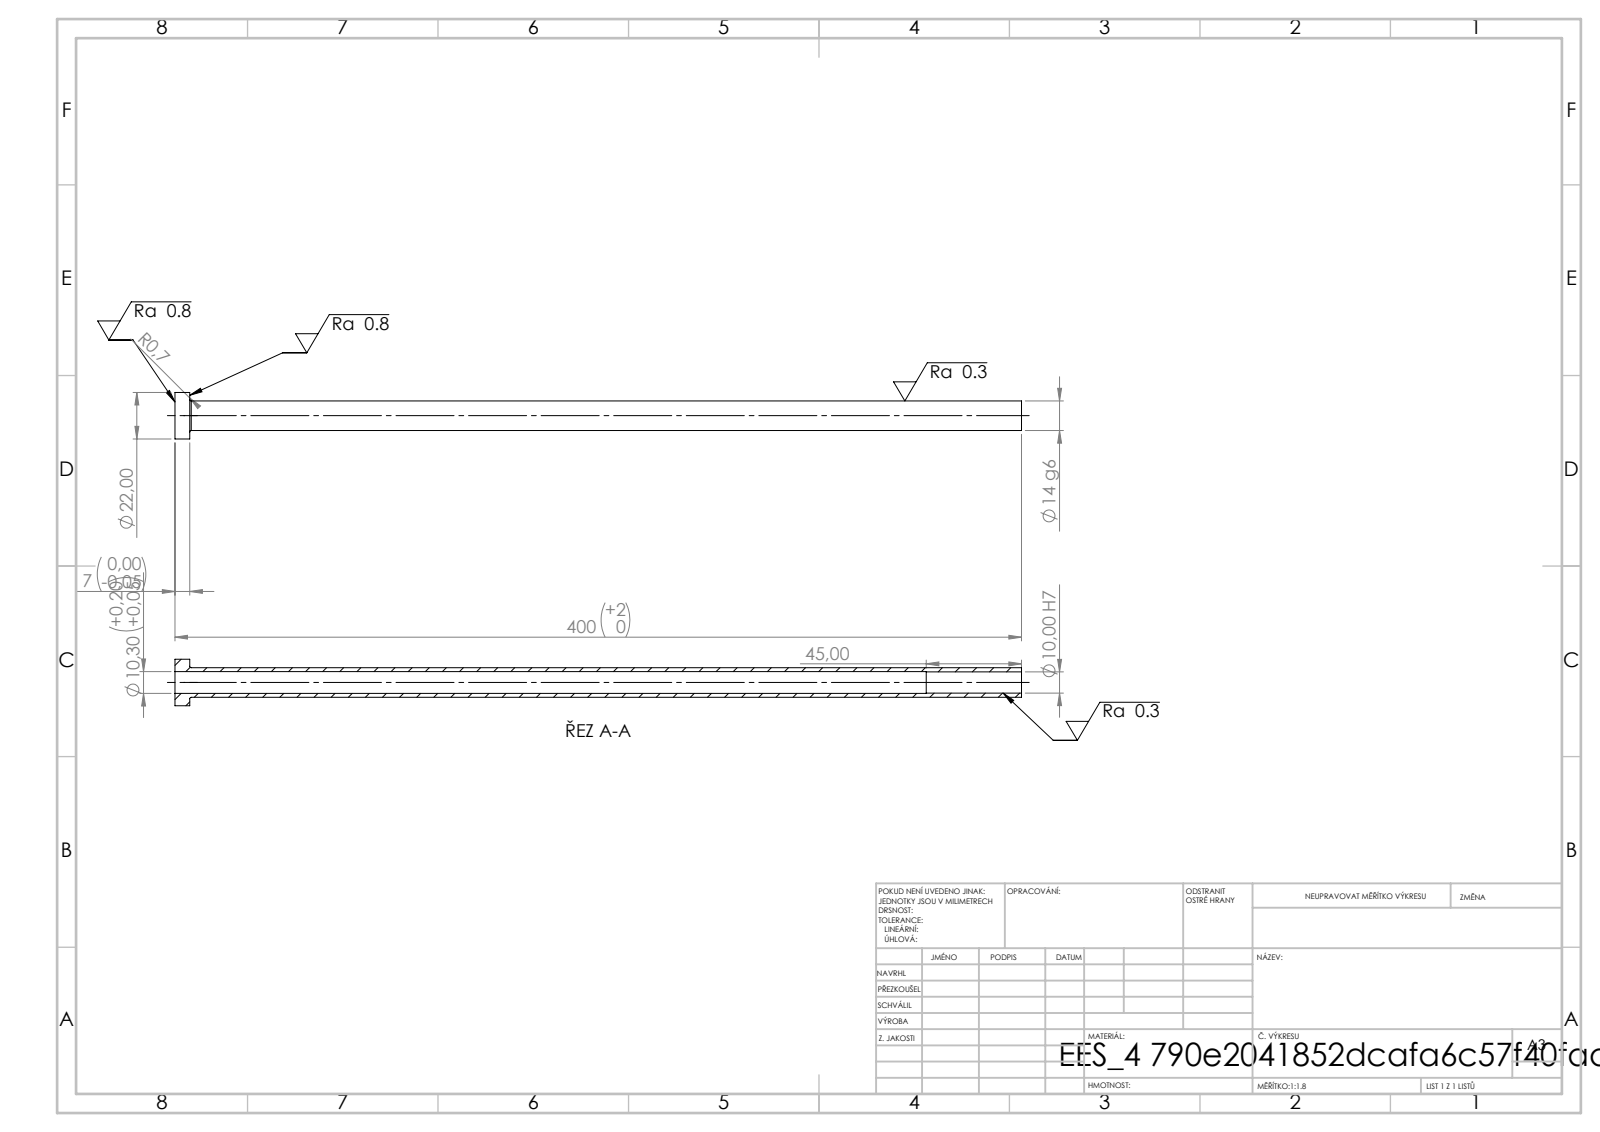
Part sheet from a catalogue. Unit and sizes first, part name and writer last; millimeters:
Units: millimetres
Overall size (bounding box): 400 × 22 × 22
Round holes (diameter × count): ⌀10 ×1, ⌀10.3 ×1
Round bosses / shafts (diameter × count): ⌀22 ×1, ⌀14 ×1
Main face-to-face distances: 7, 400, 393, 355, 348, 45
Volume: 30 049 mm³ · Surface area: 31 260 mm²
Bodies: 1 solid, 14 faces (4 planar, 8 cylindrical, 2 other)
STEP written by: SolidWorks 2019 (CONFIG_CONTROL_DESIGN)
